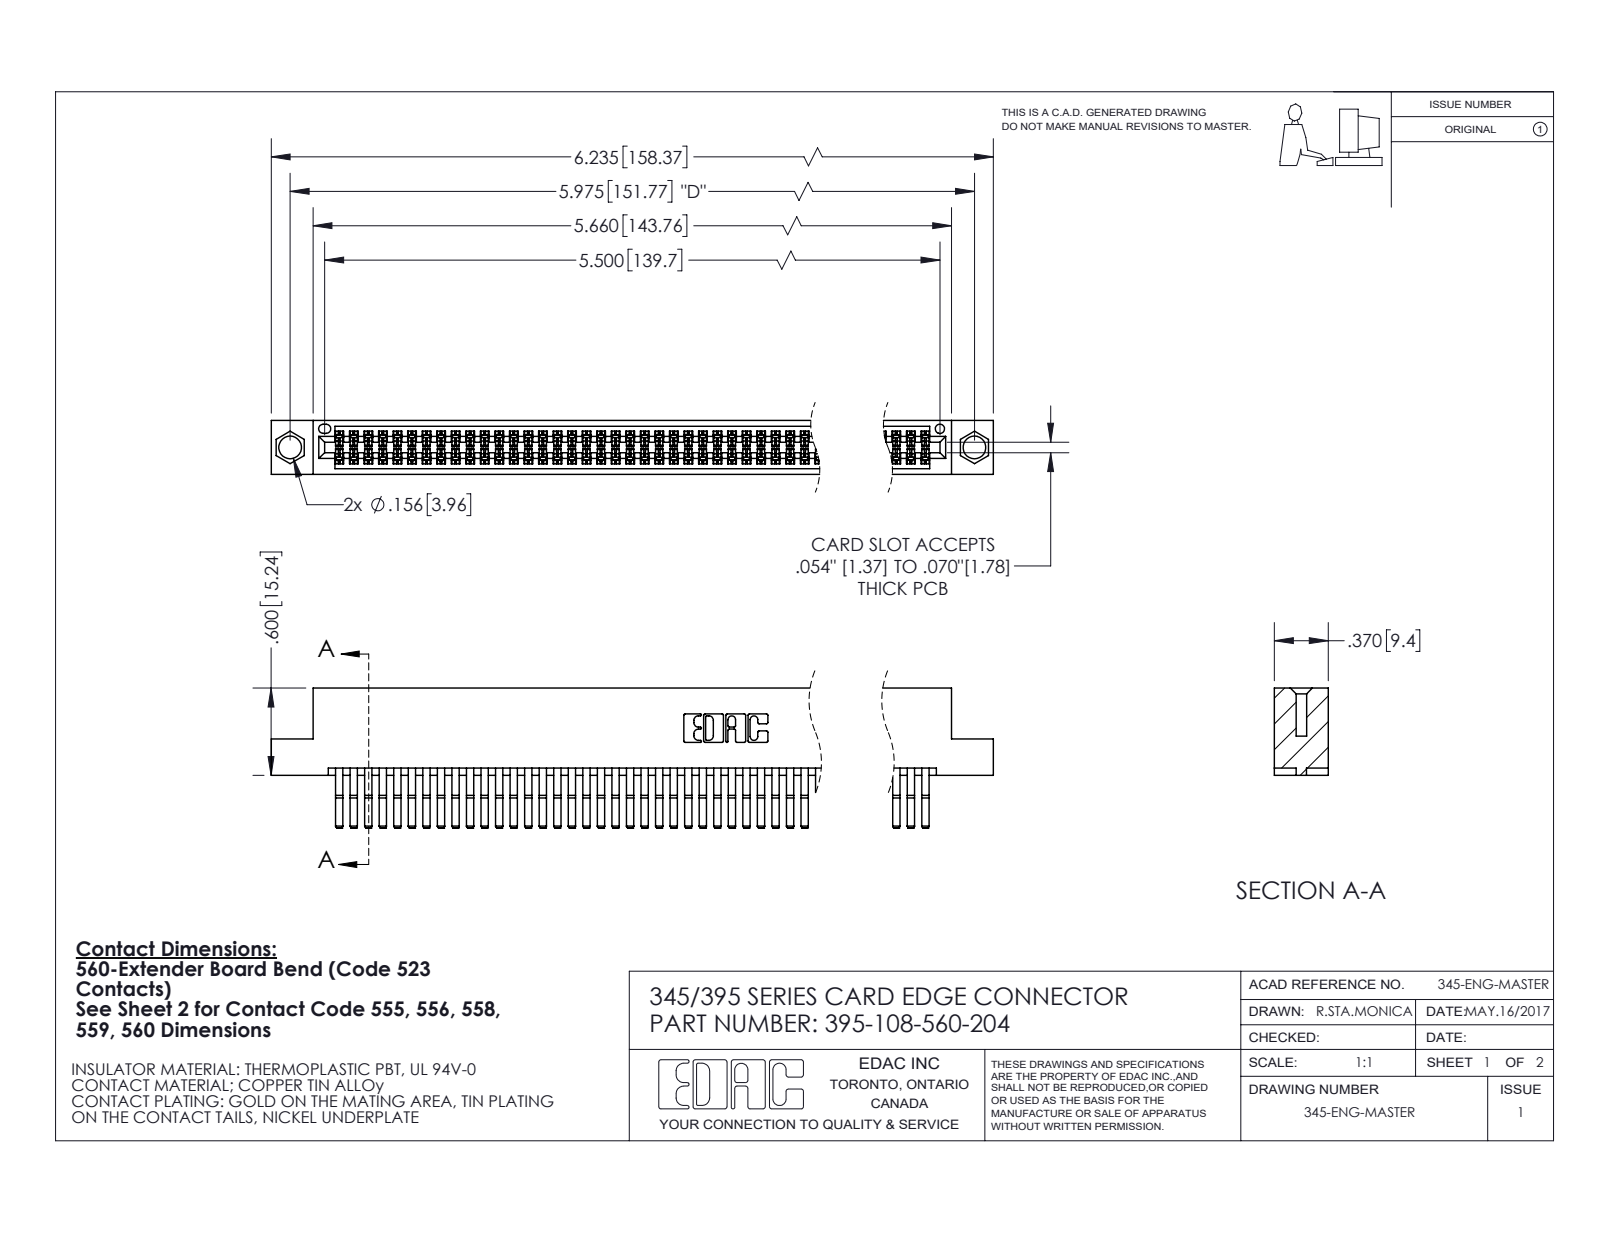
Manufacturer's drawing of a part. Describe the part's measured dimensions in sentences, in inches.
The part is named "395-108-560-204; 345-292-001_560 Tail; 345 Part_Flush Mounting Lugs - 0.156 Dia-TI". Its 3-D file was written by "SolidWorks 2020 (CONFIG_CONTROL_DESIGN)". It is 109 solids with 5756 faces: 3658 planar, 2098 cylindrical and 0 other. Overall it measures 6.235 by 0.962 by 0.37 inches. Its volume is 0.982 cubic inches and its surface area 39.83 square inches. Round holes: 2 of diameter 0.156, 1 of diameter 0.064. Partial cylindrical surfaces (rounded edges, fillets, slot ends): 216 of radius 0.006, 22 of radius 0.01, 6 of radius 0.007, 6 of radius 0.031, 3 of radius 0.026, 2 of radius 0.01, 2 of radius 0.014, 2 of radius 0.019. The main face-to-face distances are 0.025, 0.298, 0.072, 0.37, 0.2, 0.098, 0.272, 0.225, 0.175, 0.149. The hole center spacings are 0.27, 5.739, 5.975.
